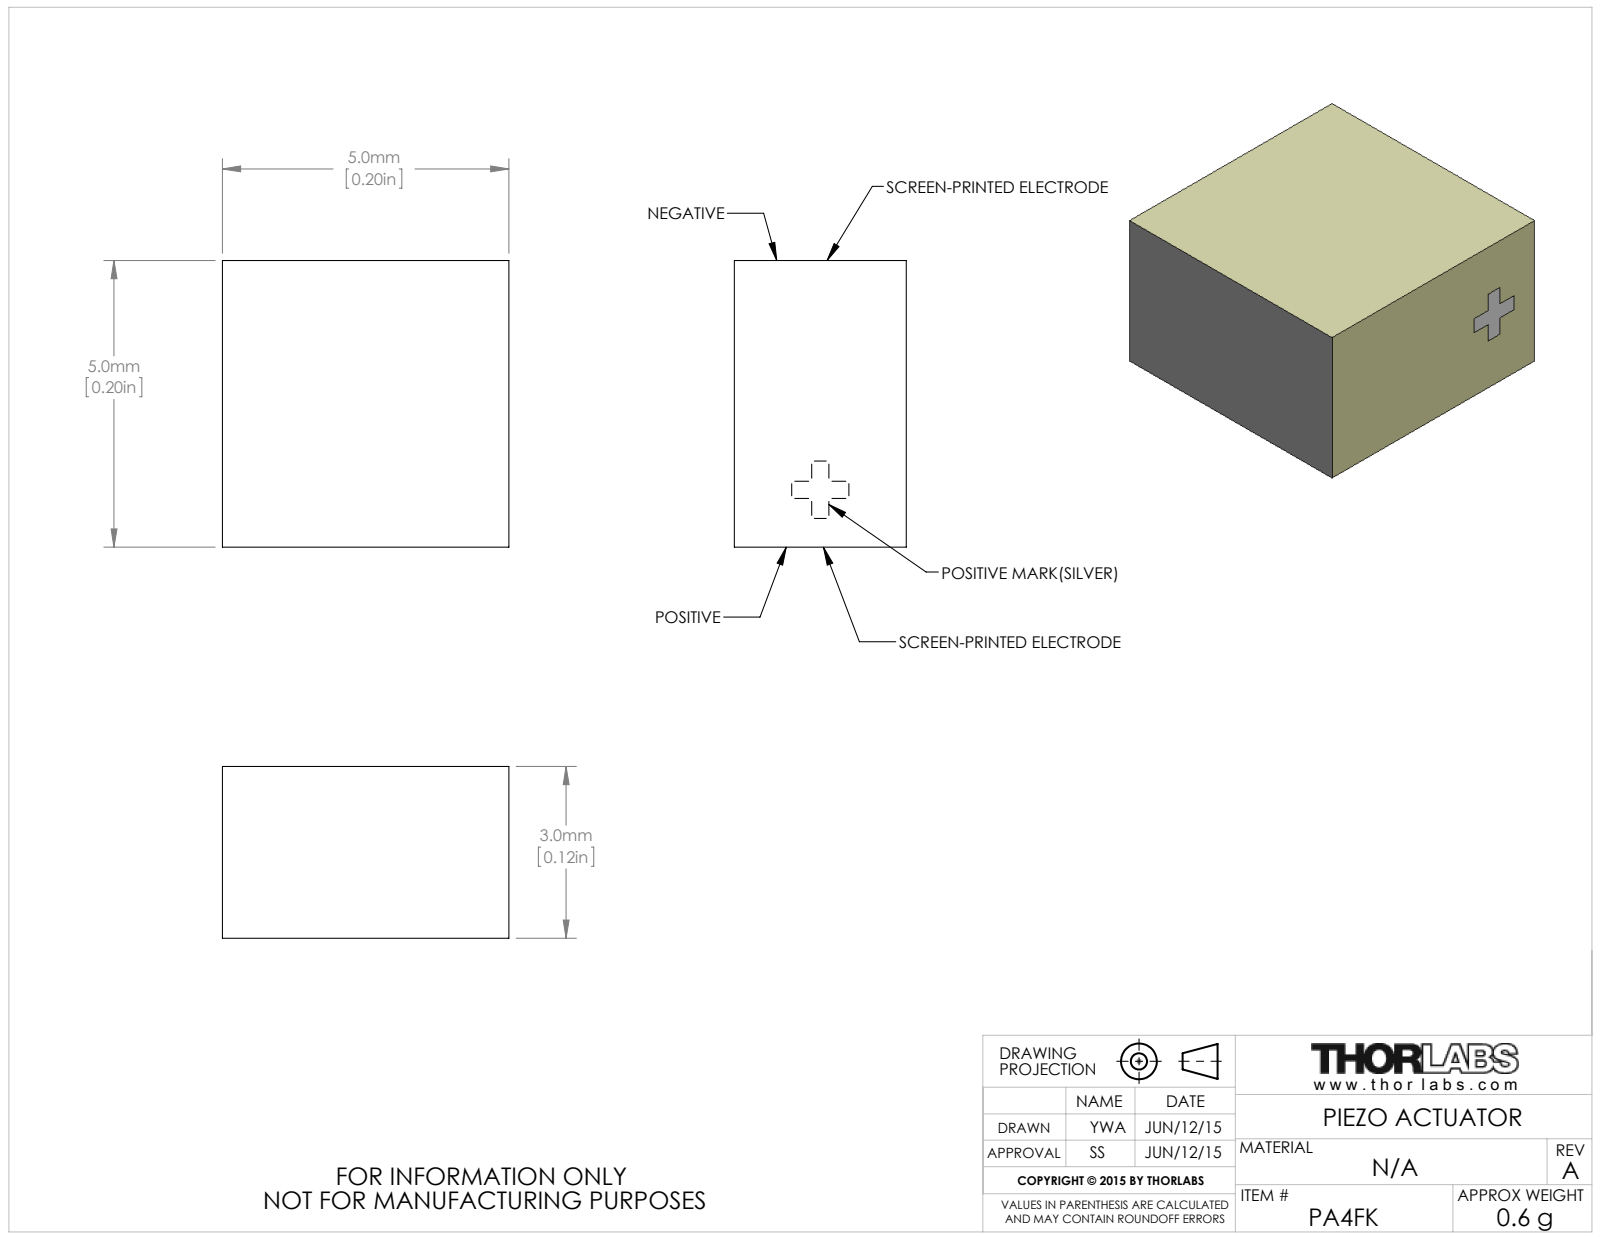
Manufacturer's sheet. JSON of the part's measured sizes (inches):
{"part_name": "CTN003019", "step_written_by": "SolidWorks 2014 (AUTOMOTIVE_DESIGN)", "units": "inches", "bodies": {"solids": 1, "faces": 7, "planar": 7, "cylindrical": 0, "other": 0}, "overall_size": [0.197, 0.197, 0.118], "volume_in3": 0.005, "surface_area_in2": 0.171, "face_to_face_distances": [0.197, 0.118]}
